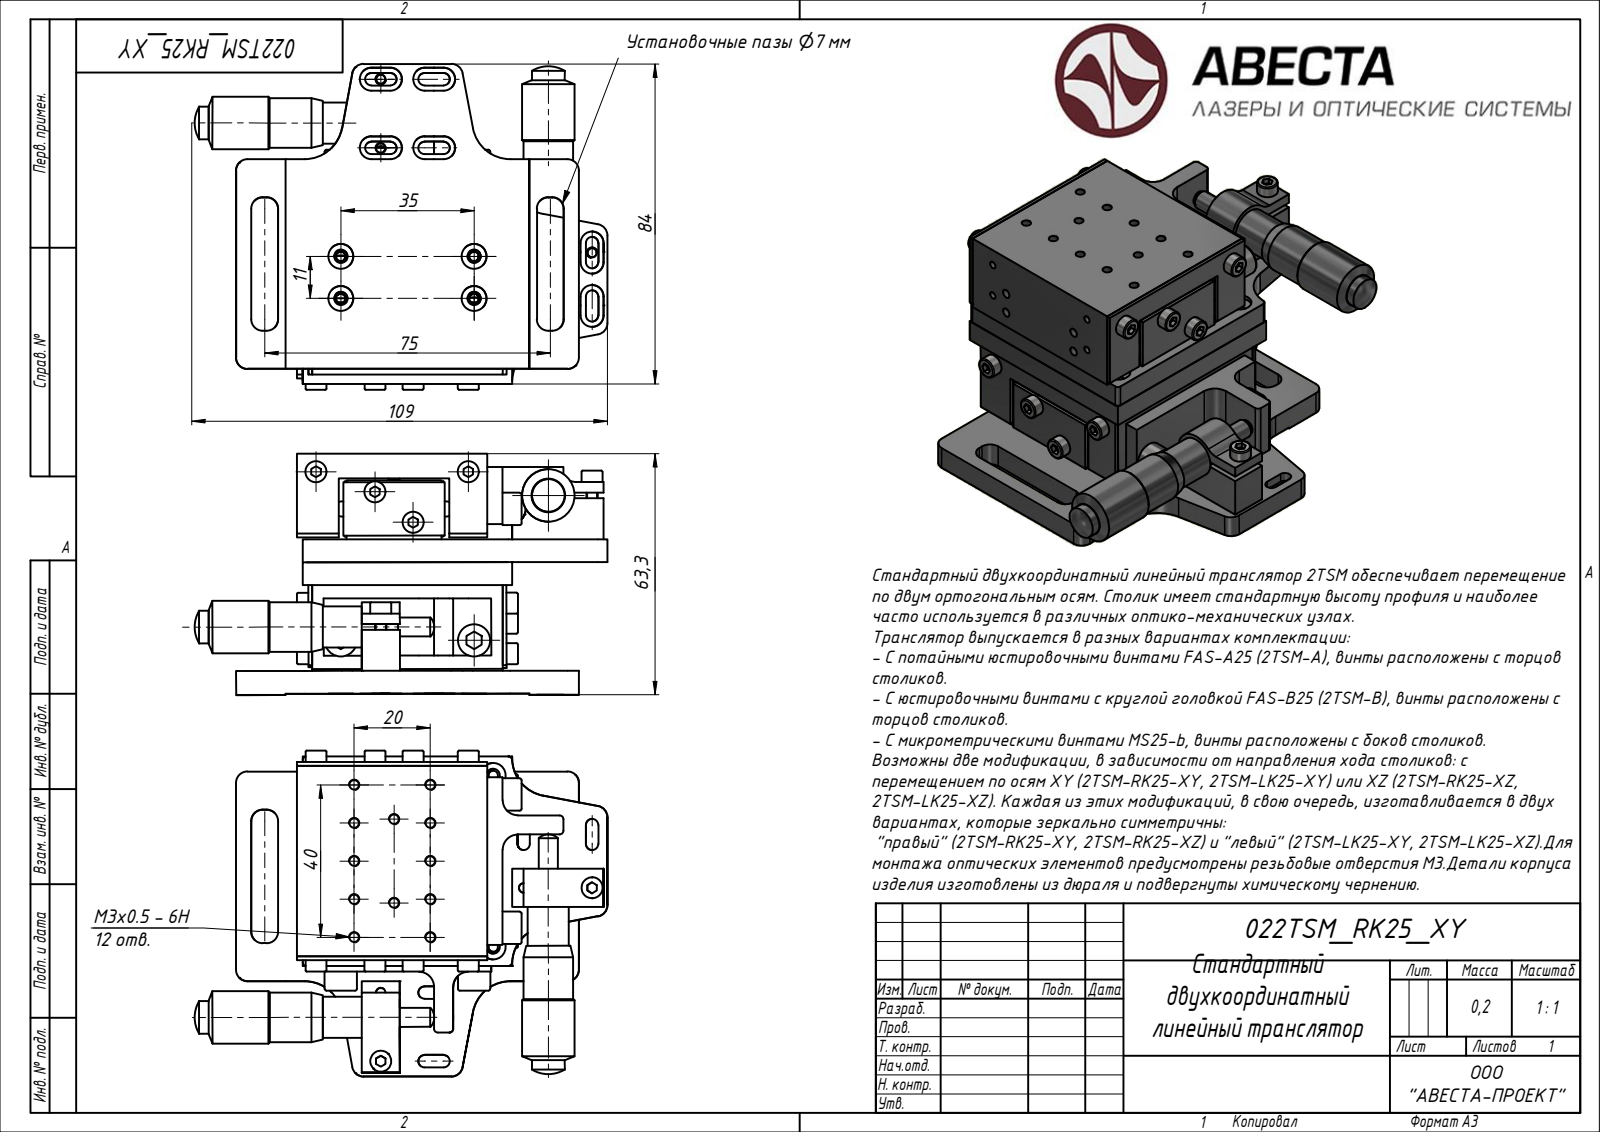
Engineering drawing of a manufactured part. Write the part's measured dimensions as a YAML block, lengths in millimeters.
part_name: "Block 03; Block 02; Block 01"
step_written_by: "ST-DEVELOPER v15 (AUTOMOTIVE_DESIGN)"
units: millimeters
bodies: {solids: 31, faces: 1387, planar: 0, cylindrical: 0, other: 1387}
overall_size: [108.41, 85.47, 63.35]
